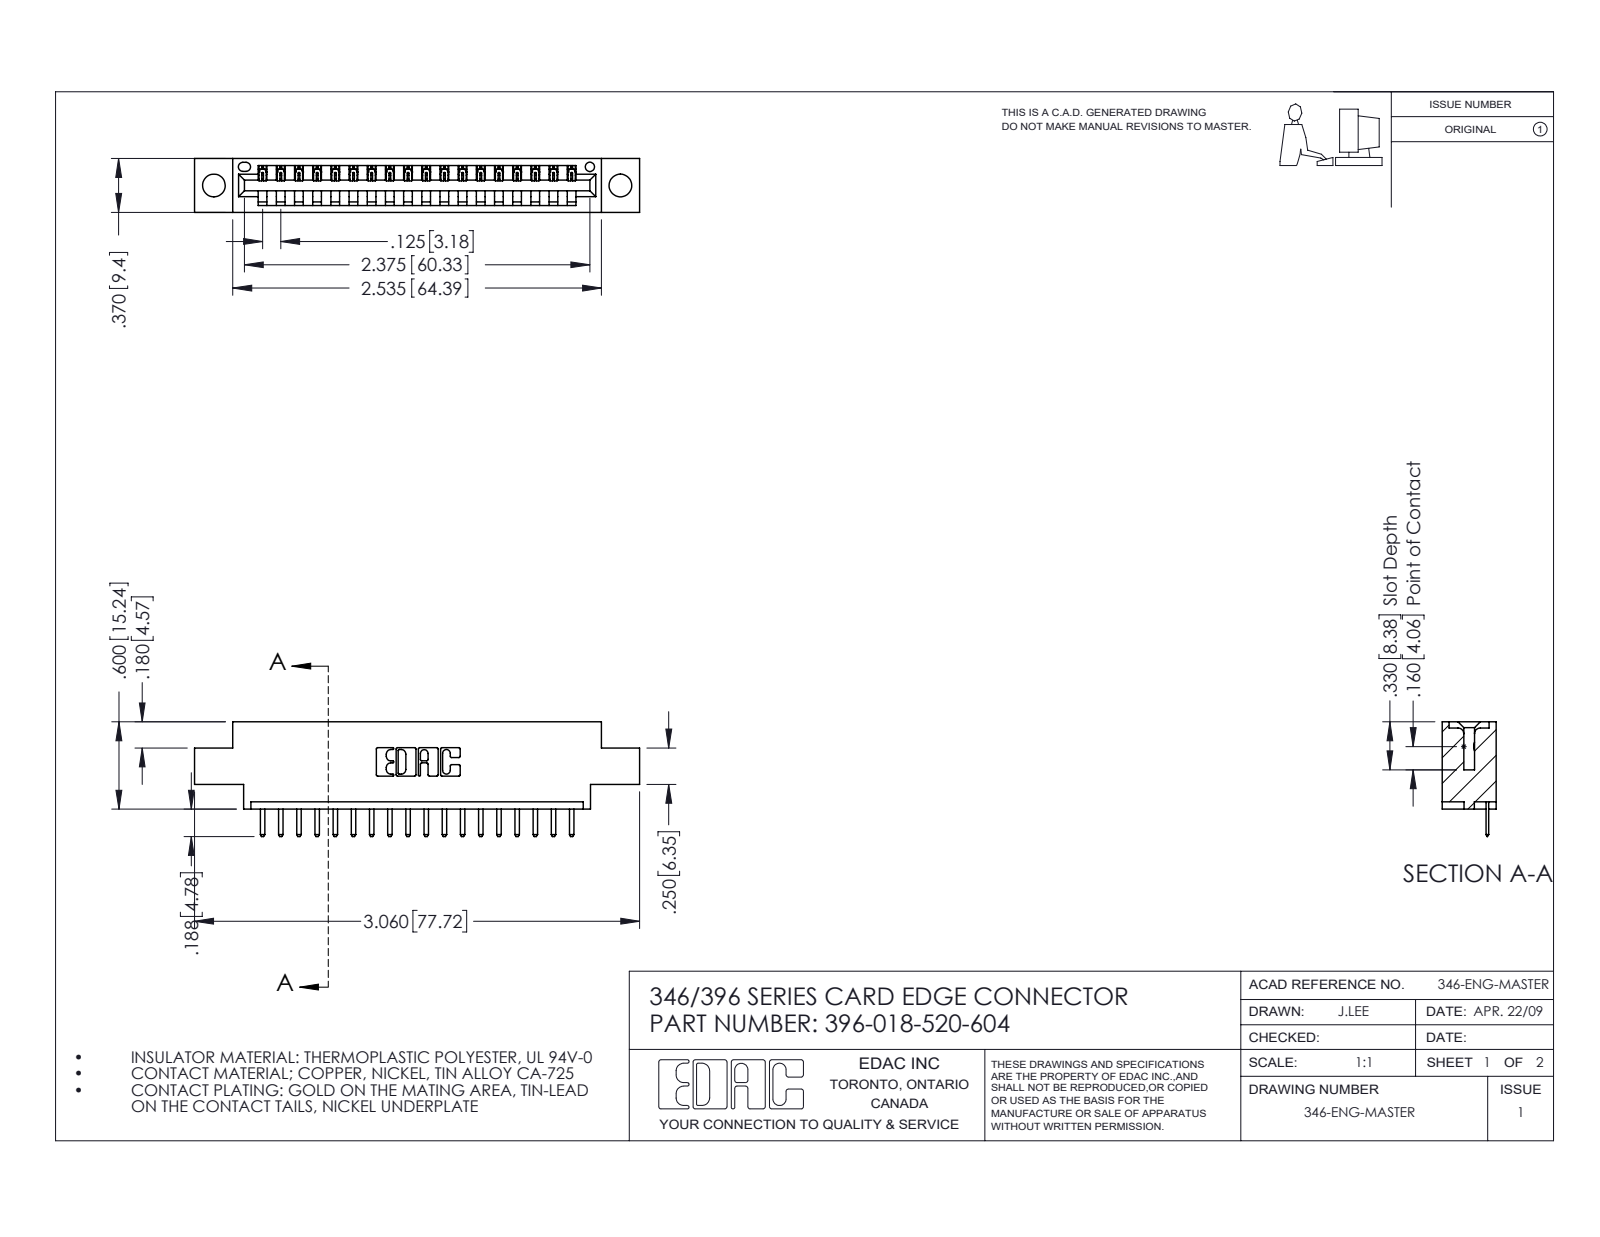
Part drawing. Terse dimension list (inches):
name: 396-018-520-604; 345-292-001_345-293-120; 346 Part_0.170 Offset - 0.156 Dia-TH
written by: SolidWorks 2016 (CONFIG_CONTROL_DESIGN)
unit: in
bodies: 19 solids, 1242 faces (836 planar, 406 cylindrical, 0 other)
size: 3.06 × 0.788 × 0.37
volume: 0.426 in³; area: 12.8 in²
holes: 2× ⌀0.156, 1× ⌀0.064
rounds: 38× R0.01, 36× R0.006, 22× R0.01, 6× R0.007, 6× R0.031, 3× R0.026, 2× R0.031, 2× R0.04
face distances: 0.37, 0.048, 0.322, 0.25, 0.148, 0.222, 0.1, 0.174, 0.072, 0.298
hole spacings: 0.246, 2.588, 2.795
